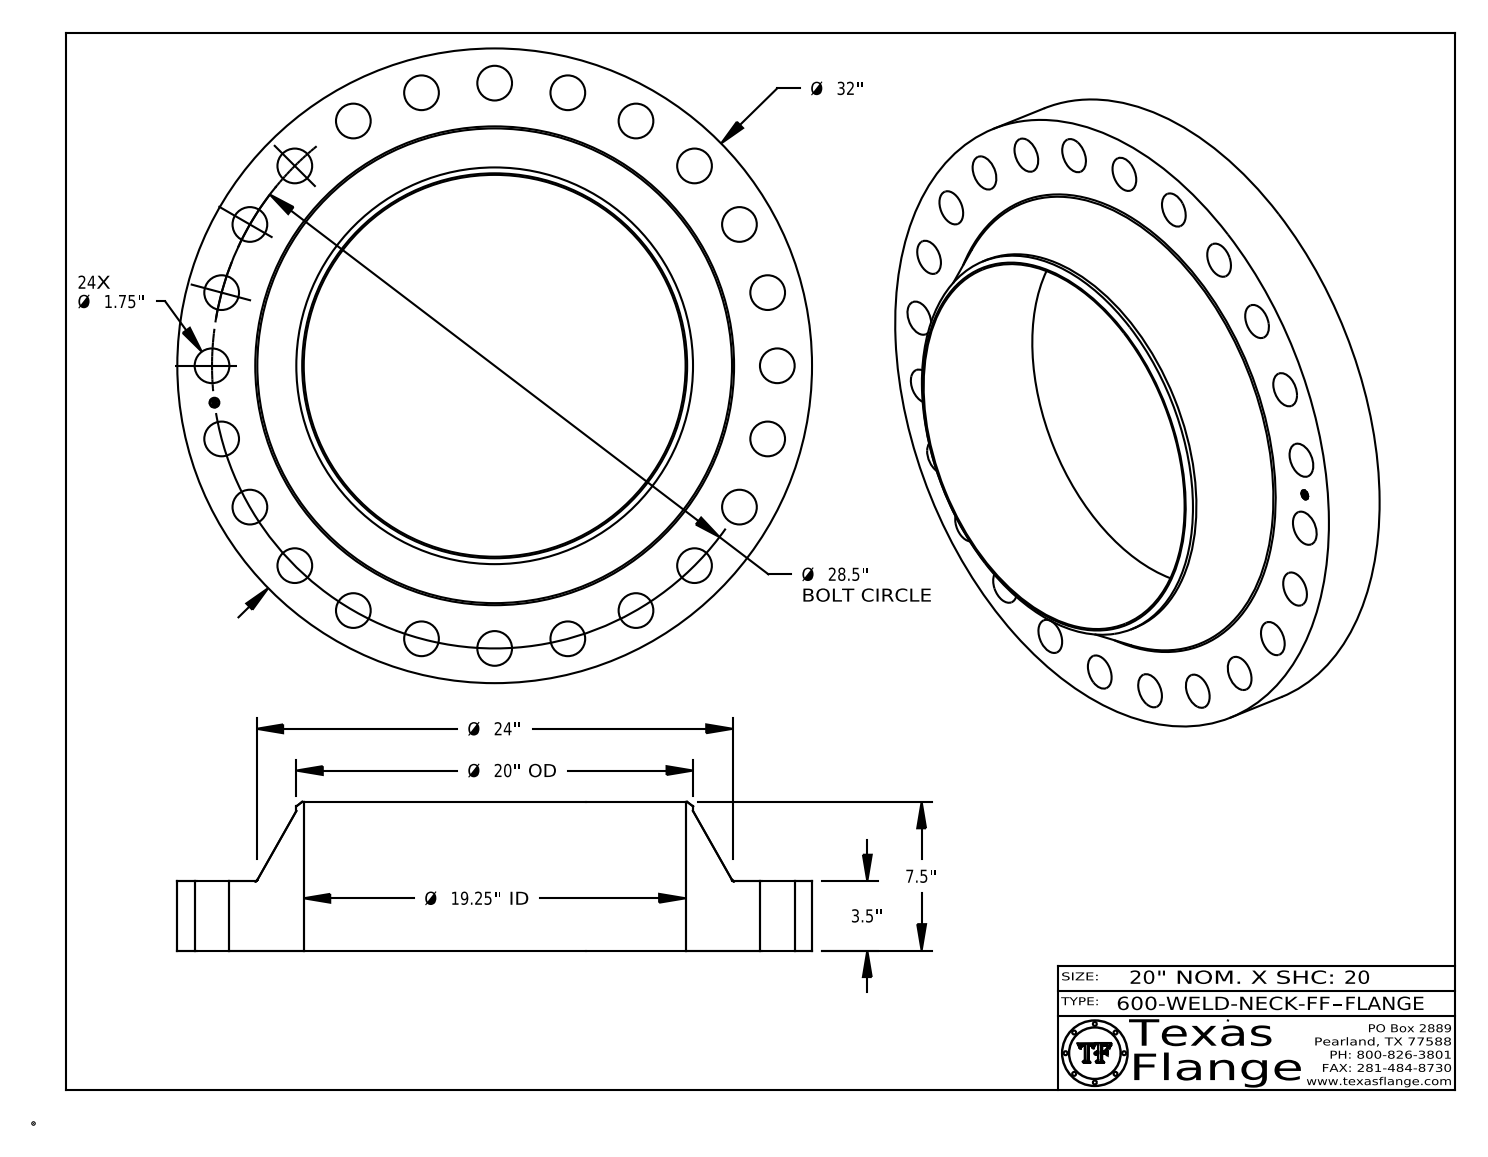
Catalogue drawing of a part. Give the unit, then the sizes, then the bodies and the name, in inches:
Units: inches
Overall size (bounding box): 32 × 32 × 7.5
Round holes (diameter × count): ⌀1.75 ×24, ⌀0.495 ×1, ⌀19.25 ×1
Round bosses / shafts (diameter × count): ⌀0.03 ×8, ⌀32 ×1, ⌀20 ×1, ⌀0.39 ×1
Main face-to-face distances: 3.5, 7.5, 4, 0.015, 3.485, 4.015, 0.148, 0.145, 0.027, 0.096
Hole centre spacings: 14.25, 3.72, 7.376, 24.682, 26.331, 27.529, 20.153, 10.907
Volume: 1 922 in³ · Surface area: 2 339 in²
Bodies: 1 solid, 448 faces (368 planar, 74 cylindrical, 6 other)
Part name (STEP PRODUCT): 600-WELD-NECK-FF
STEP written by: CATIA V5 STEP AP214 (AUTOMOTIVE_DESIGN)
